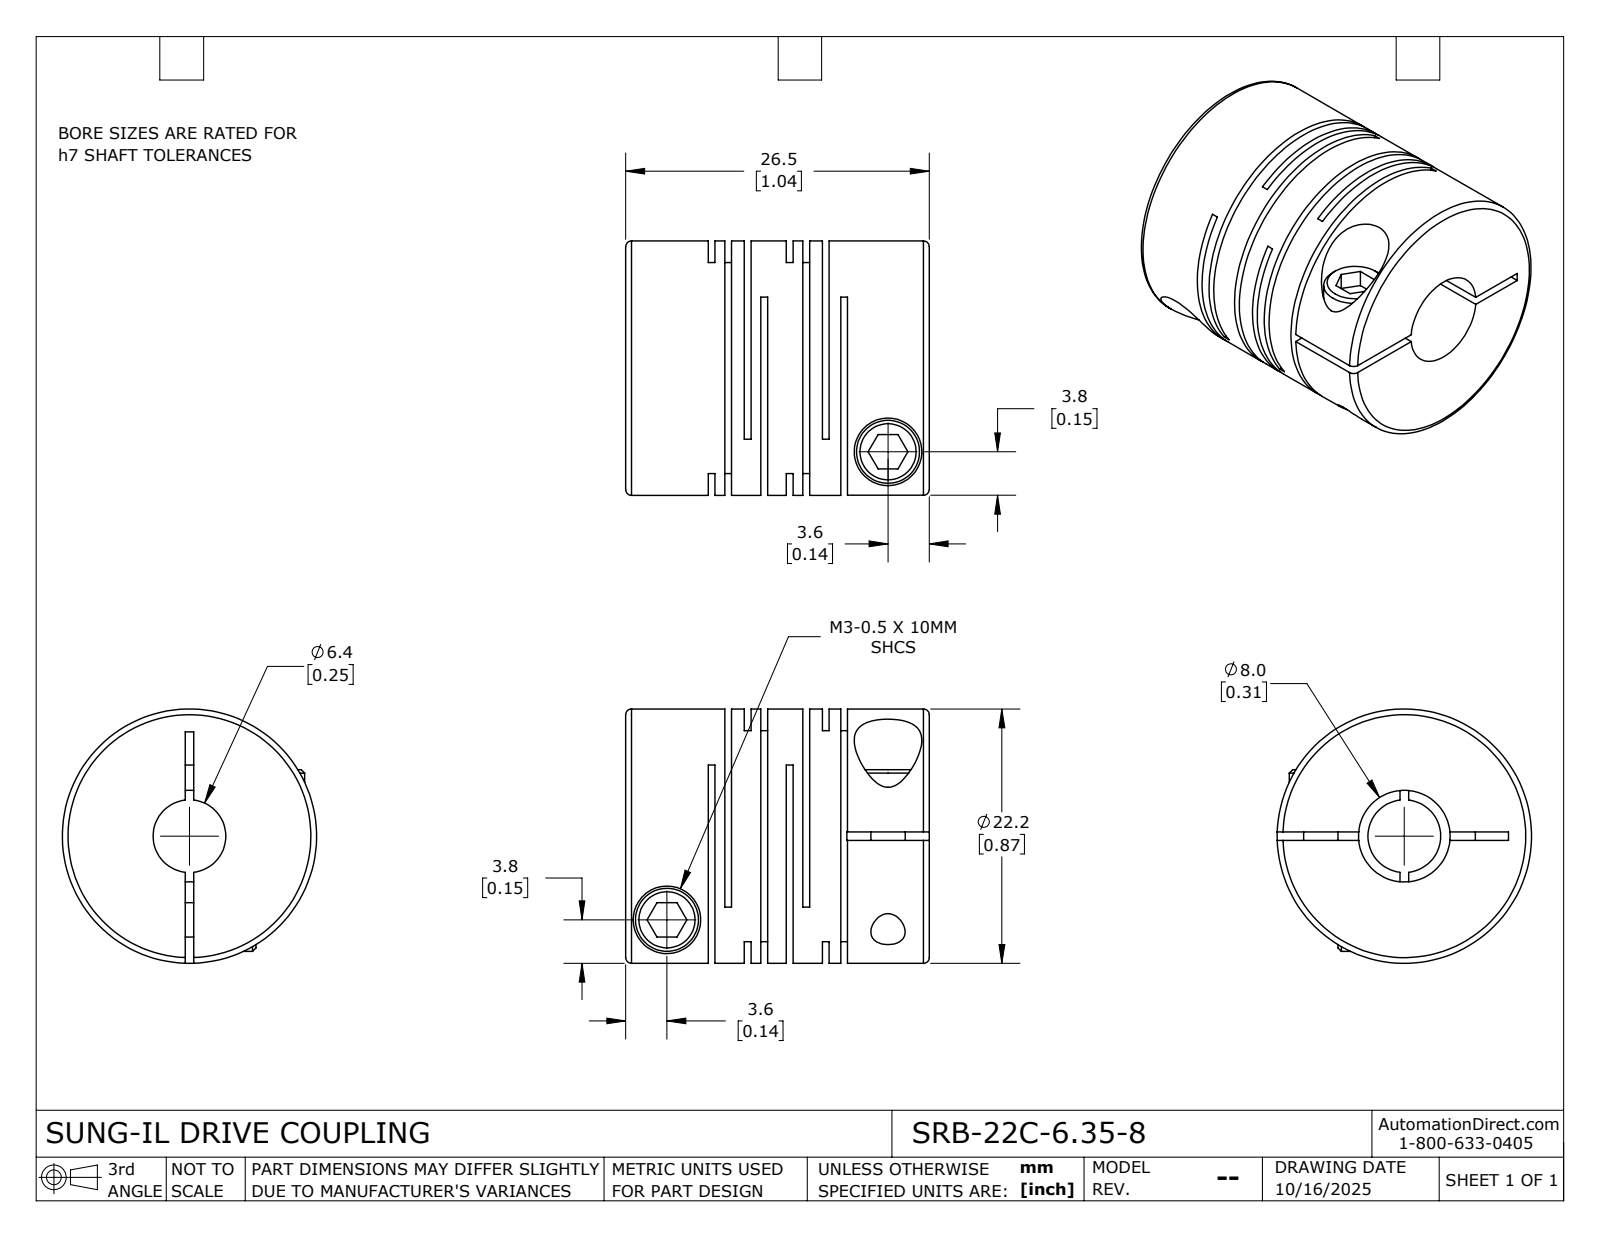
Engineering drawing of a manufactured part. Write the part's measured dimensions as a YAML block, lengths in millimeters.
part_name: "SRB-22C-6.35-8"
step_written_by: "SolidWorks 2024 (CONFIG_CONTROL_DESIGN)"
units: millimeters
bodies: {solids: 1, faces: 115, planar: 60, cylindrical: 42, other: 13}
overall_size: [26.5, 22.2, 22.2]
volume: 7441
surface_area: 7862
round_holes:
  - {diameter: 3, count: 2}
  - {diameter: 5.9, count: 2}
  - {diameter: 6.35, count: 1}
  - {diameter: 8, count: 1}
round_bosses_or_shafts:
  - {diameter: 5.5, count: 2}
  - {diameter: 22.2, count: 1}
face_to_face_distances: [0.59, 6.82, 1.45, 3.15, 5.37, 1.7, 3.67, 2.04, 7.41, 6.23]
